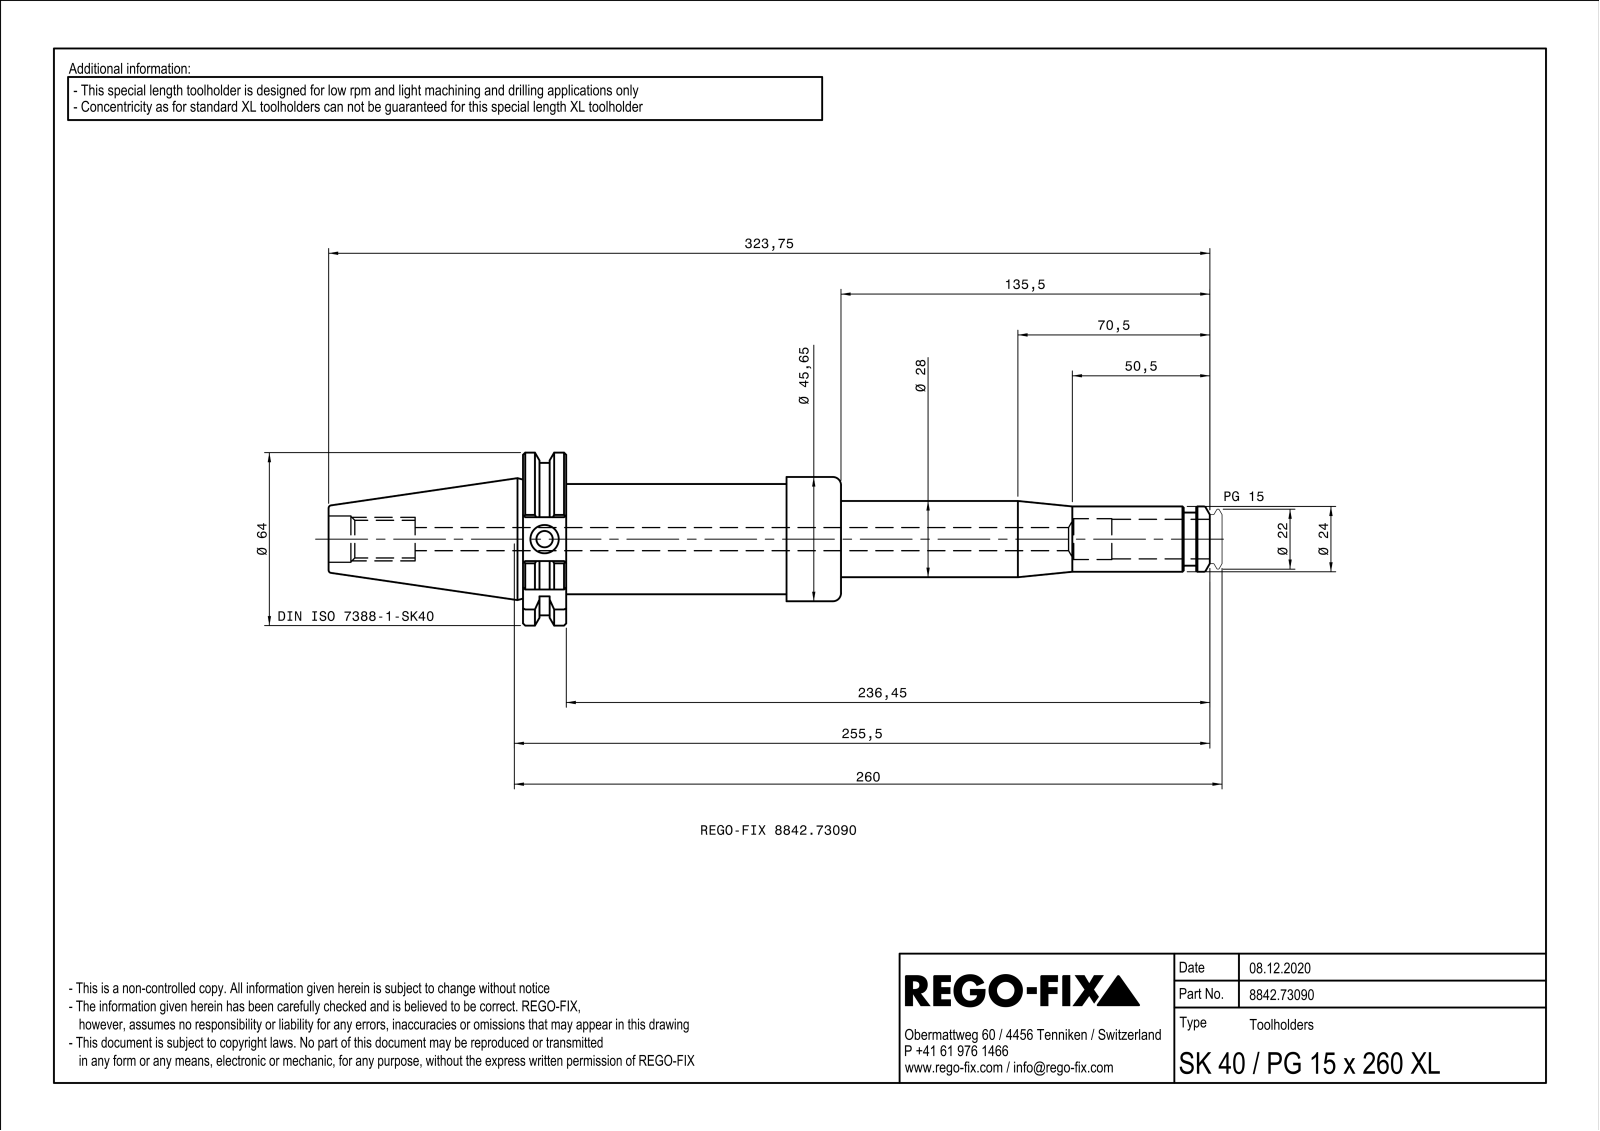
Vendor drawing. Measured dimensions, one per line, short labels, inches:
name: NOCUT
written by: SIEMENS PLM Software Solid Edge ST10 (AUTOMOTIVE_DESIGN)
unit: in
bodies: 1 solid, 175 faces (56 planar, 48 cylindrical, 71 other)
size: 12.746 × 2.502 × 2.402
volume: 16.45 in³; area: 95.2 in²
holes: 2× ⌀0.394, 1× ⌀0.236, 1× ⌀0.354, 1× ⌀0.512, 1× ⌀0.545, 1× ⌀0.591, 1× ⌀0.669, 1× ⌀0.984, 1× ⌀1.142, 1× ⌀1.511, 1× ⌀1.577, 1× ⌀1.705
bosses: 1× ⌀1.797, 1× ⌀1.594, 1× ⌀1.575, 1× ⌀1.339, 1× ⌀1.299, 1× ⌀1.102, 1× ⌀0.972, 1× ⌀0.945
rounds: 13× R0.02, 1× R0.896, 1× R1.102, 1× R1.251
face distances: 0.624, 3.974, 4.598, 0.236, 0.551, 0.059, 3.915, 4.539, 0.787, 0.728
